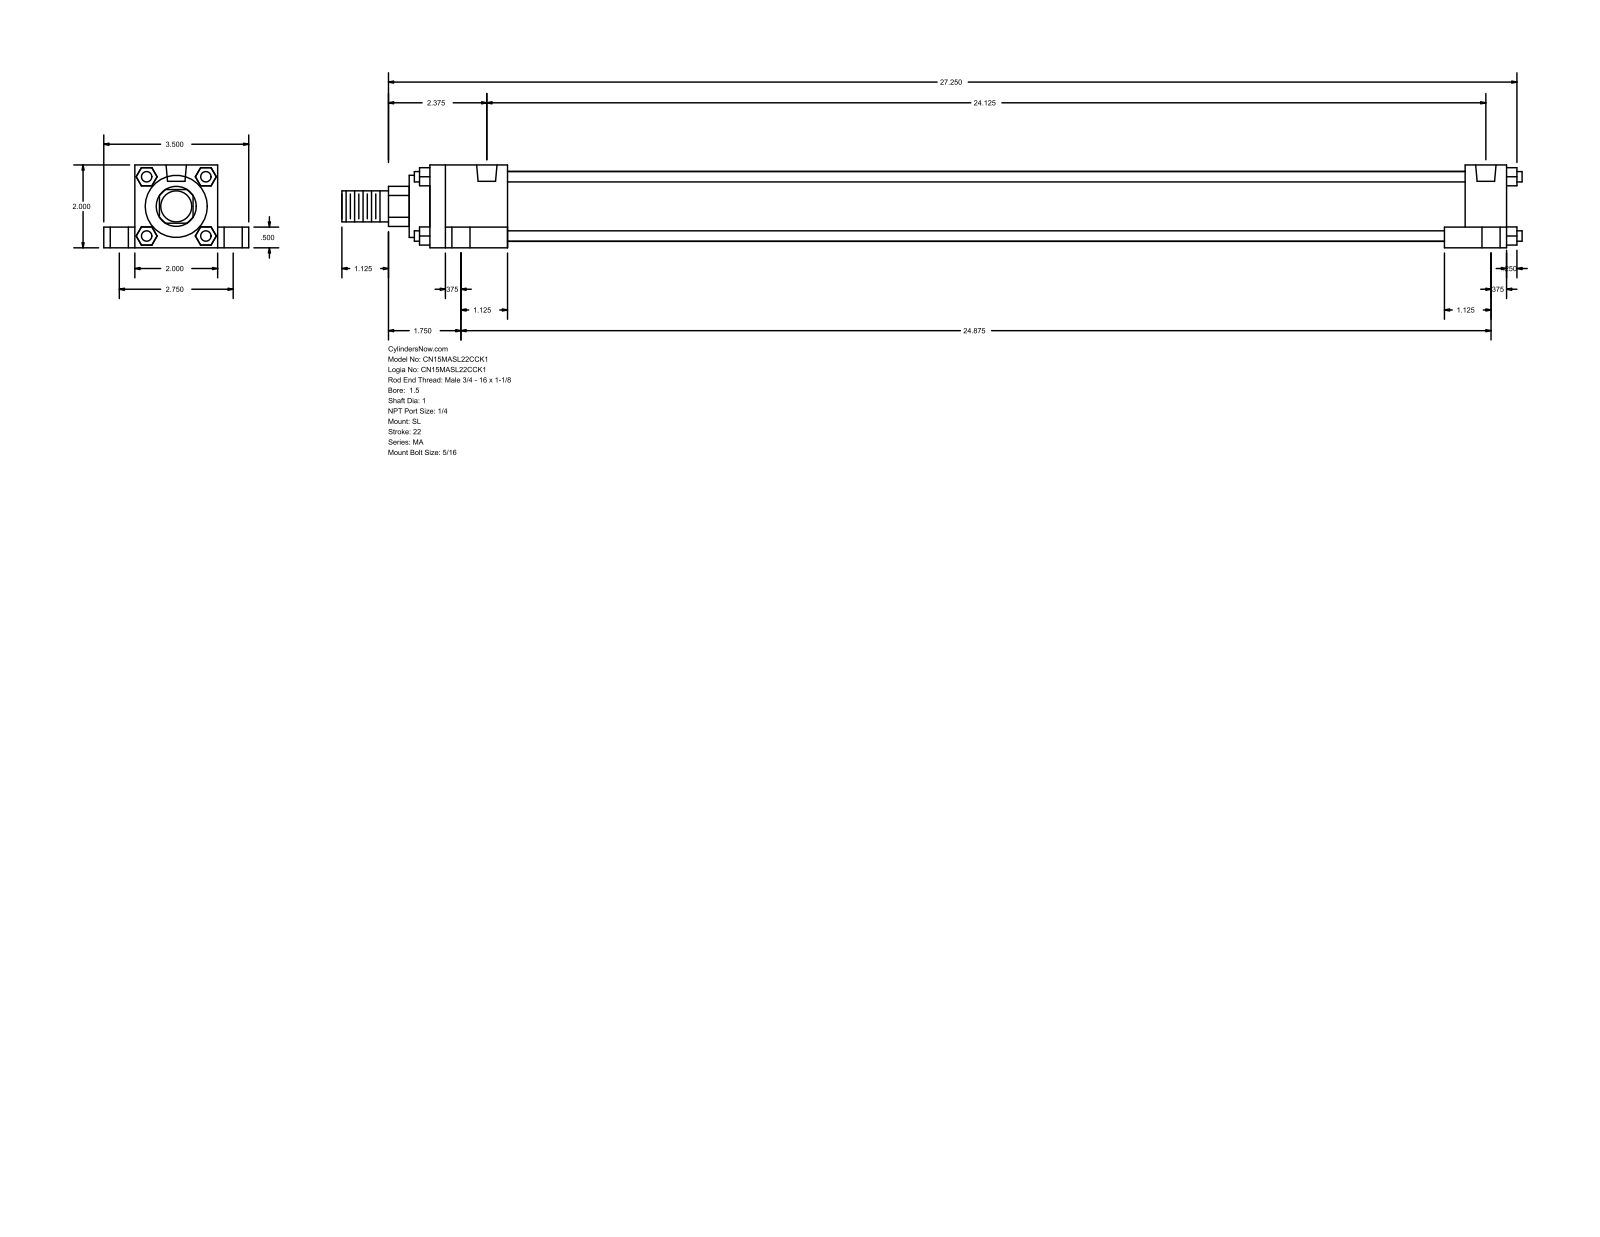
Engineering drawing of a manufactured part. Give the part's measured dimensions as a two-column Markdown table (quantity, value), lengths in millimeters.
| quantity | value |
| --- | --- |
| part name | MA_SL__0150_1 |
| STEP written by | GSSL Pune (CONFIG_CONTROL_DESIGN) |
| units | millimeters |
| bodies | 0 solids, 148 faces (112 planar, 36 cylindrical, 0 other) |
| overall size | 723.9 × 88.9 × 50.8 |
| round holes (diameter × count) | 7.94 × 4, 11.11 × 4, 17.46 × 4, 12.49 × 2 |
| round bosses / shafts (diameter × count) | 6.35 × 4, 42.93 × 1, 38.1 × 1, 25.4 × 1, 19.05 × 1 |
| partial cylindrical surfaces (radius × count) | 12.29 × 1 |
| main face-to-face distances | 50.8, 12.7, 19.05, 69.85, 38.1, 9.52, 660.4, 25.4, 6.35, 635 |
| hole center spacings | 35.06, 38.36, 69.84, 612.77, 616.93, 629.62, 631.82, 635.67 |
